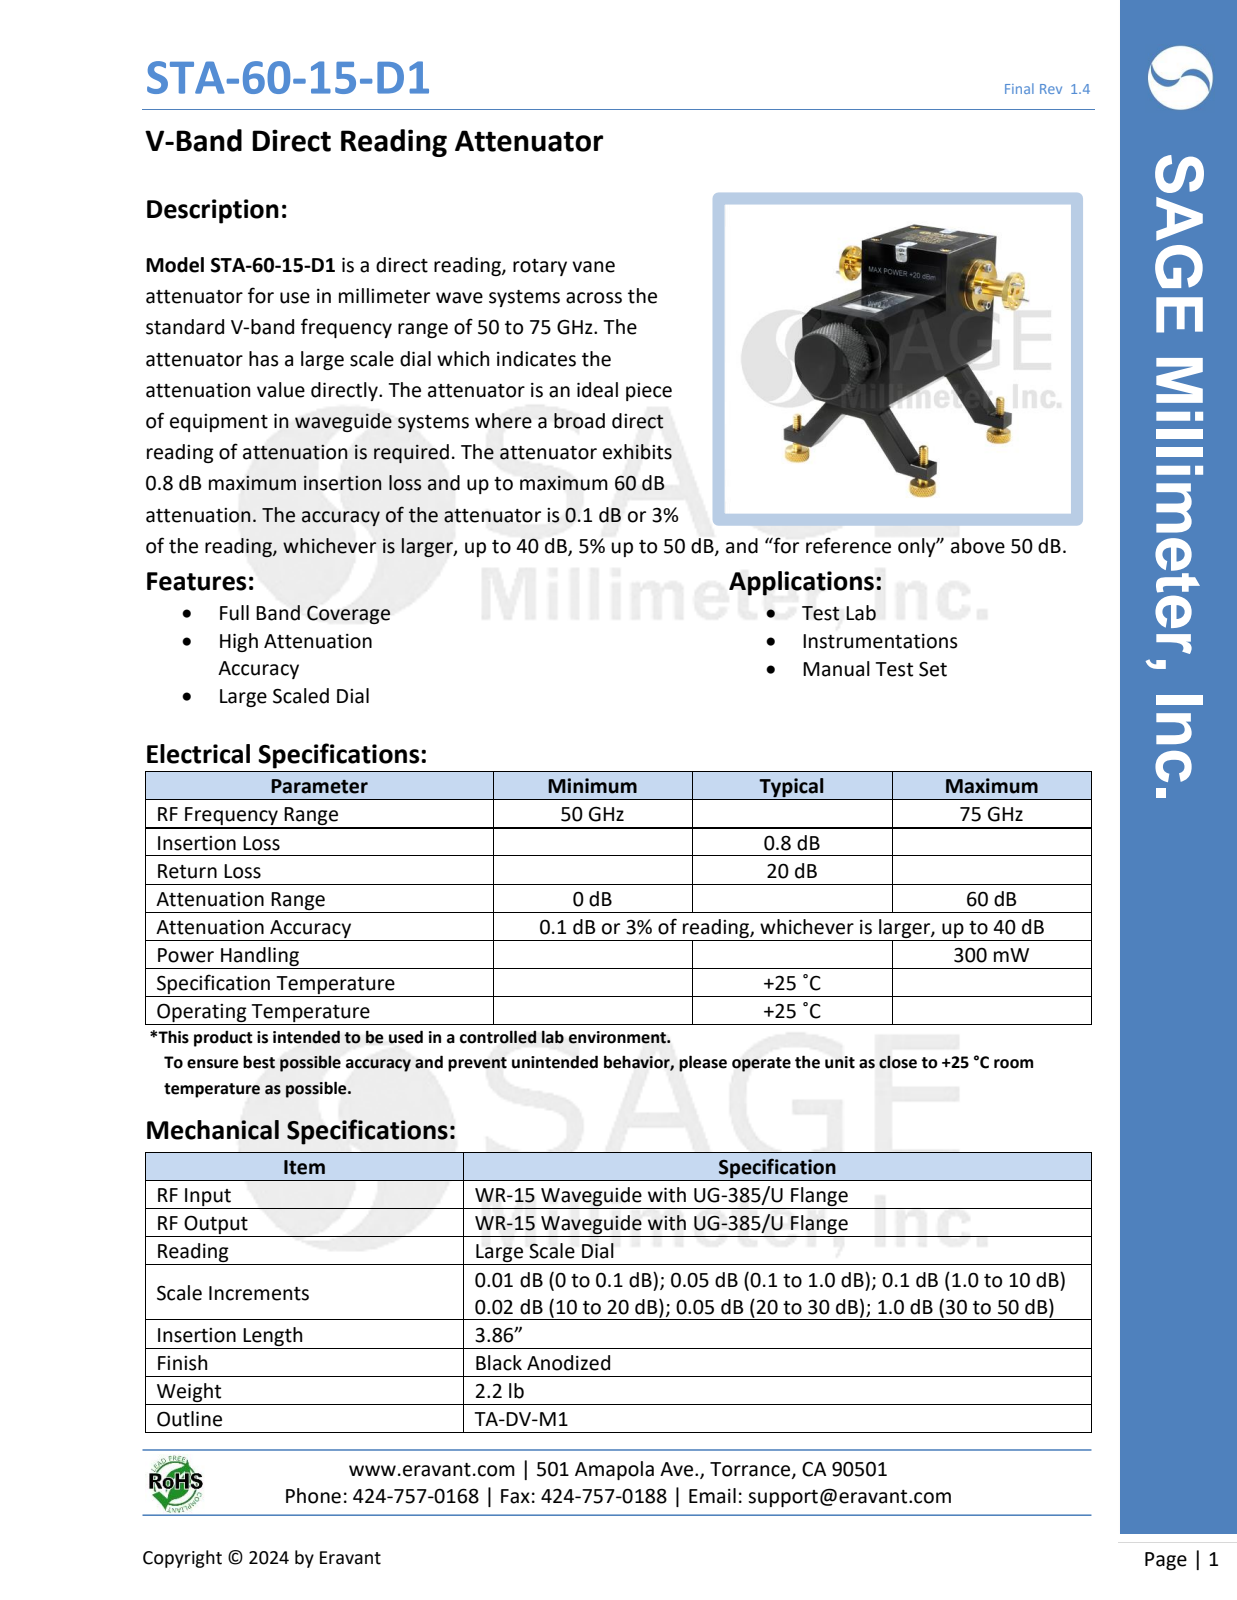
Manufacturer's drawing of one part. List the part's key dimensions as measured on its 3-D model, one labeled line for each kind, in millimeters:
Part name (STEP PRODUCT): STA-60-15-D1
STEP written by: SolidWorks 2016 (CONFIG_CONTROL_DESIGN)
Units: millimetres
Bodies: 16 solids, 1613 faces (780 planar, 234 cylindrical, 599 other)
Overall size (bounding box): 121.16 × 118.49 × 105.03
Volume: 347 288 mm³ · Surface area: 49 810 mm²
Round holes (diameter × count): ⌀1.51 ×8, ⌀1.7 ×8, ⌀2.26 ×8, ⌀3.56 ×8, ⌀3.8 ×4
Round bosses / shafts (diameter × count): ⌀1.59 ×8, ⌀12.7 ×5, ⌀4.83 ×4, ⌀31.75 ×1, ⌀28.58 ×1, ⌀19.05 ×1, ⌀12.01 ×1, ⌀9.53 ×1
Main face-to-face distances: 50.8, 6.35, 69.85, 22.86, 46.99, 10.16, 16.51, 85.09, 95.25, 78.74
Hole centre spacings: 8.52, 13.89, 5.47, 9.11, 17.69, 17.7, 19.05, 22
